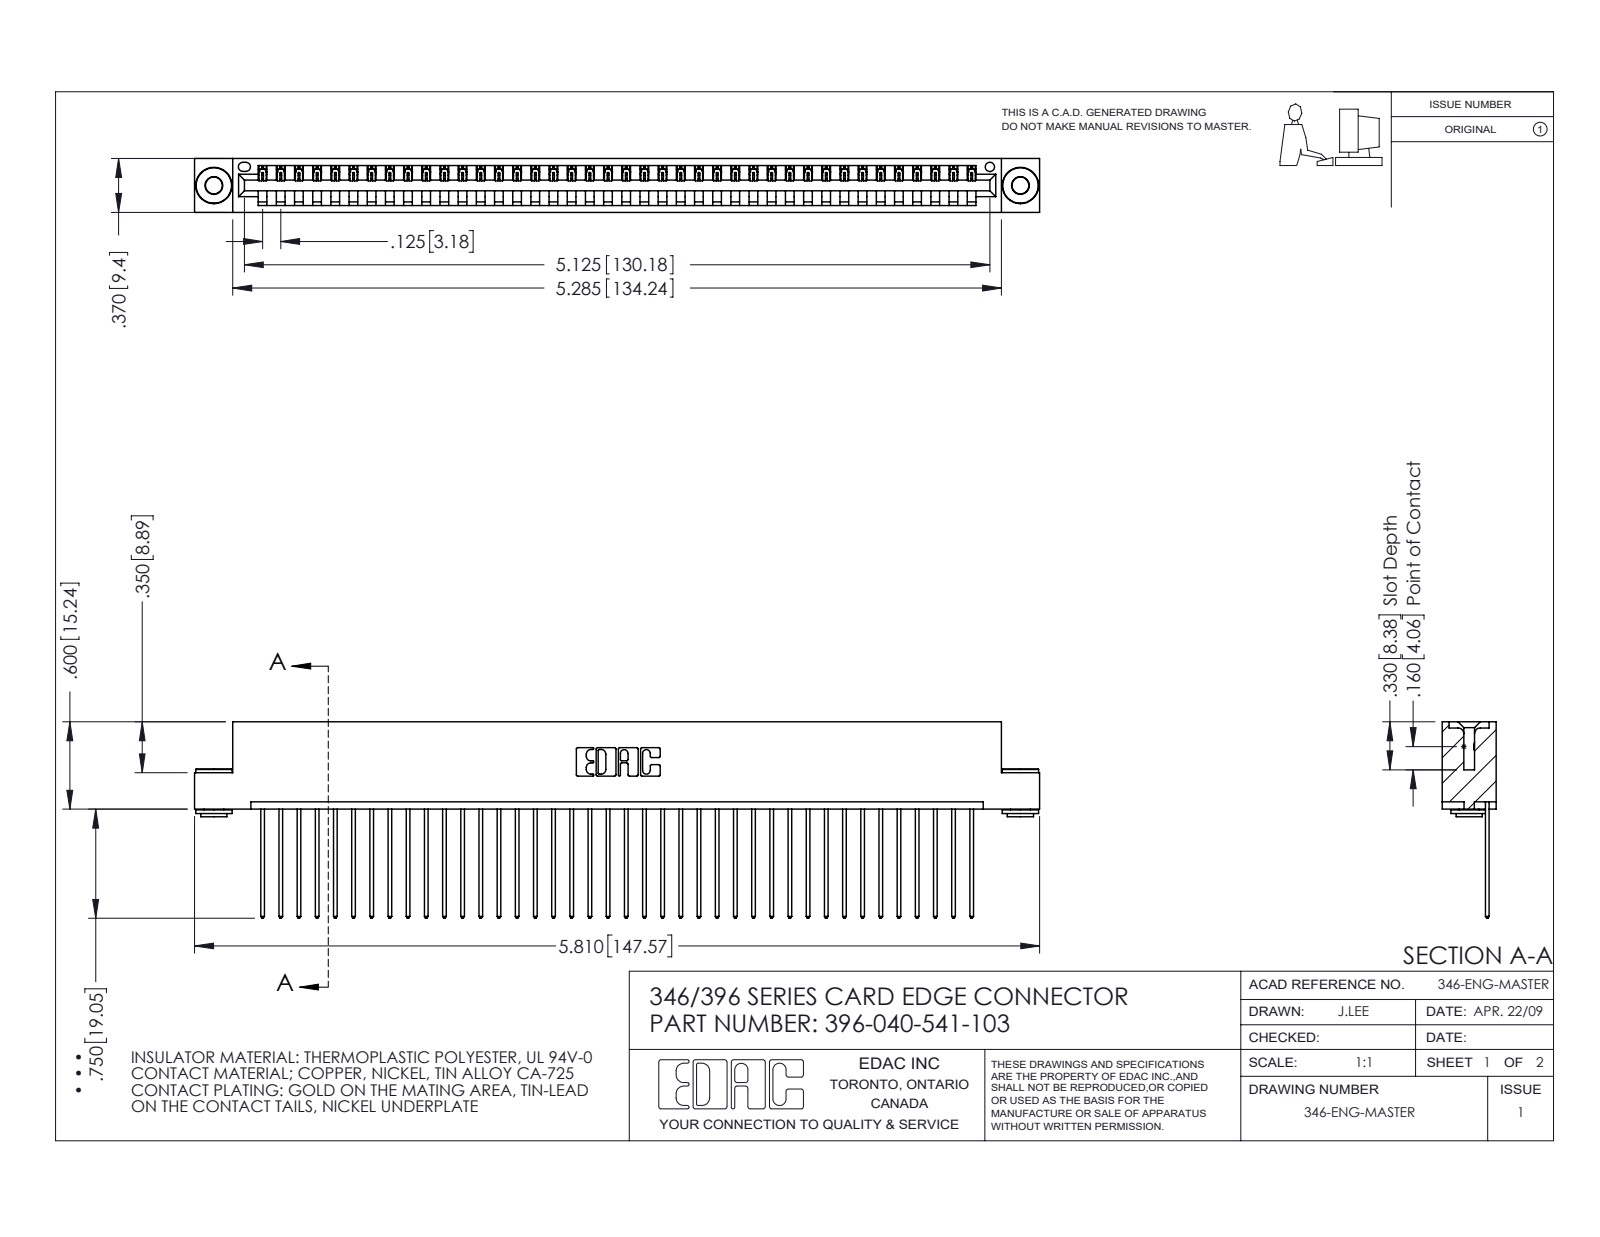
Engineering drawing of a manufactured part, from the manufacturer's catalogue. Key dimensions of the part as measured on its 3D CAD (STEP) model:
Part name (STEP PRODUCT): 345-250-002_345-250-002-102; 345-292-001_345-293-141; 396-040-541-103; 346 Part_Flush Mounting Lugs - 0.156 Dia-TH
STEP written by: SolidWorks 2016 (CONFIG_CONTROL_DESIGN)
Units: inches
Bodies: 43 solids, 2480 faces (1686 planar, 786 cylindrical, 8 other)
Overall size (bounding box): 5.81 × 1.35 × 0.37
Volume: 0.87 in³ · Surface area: 29.16 in²
Round holes (diameter × count): ⌀0.116 ×2, ⌀0.156 ×2, ⌀0.064 ×1
Round bosses / shafts (diameter × count): ⌀0.25 ×2, ⌀0.18 ×2, ⌀0.136 ×2
Partial cylindrical surfaces — rounded edges, fillets, slot ends (radius × count): R0.006 ×80, R0.01 ×80, R0.01 ×22, R0.007 ×6, R0.031 ×6, R0.026 ×3, R0.031 ×2, R0.04 ×2
Main face-to-face distances: 0.048, 0.322, 0.37, 0.25, 0.025, 0.072, 0.298, 0.148, 0.222, 0.1
Hole centre spacings: 0.246, 5.336, 5.545
